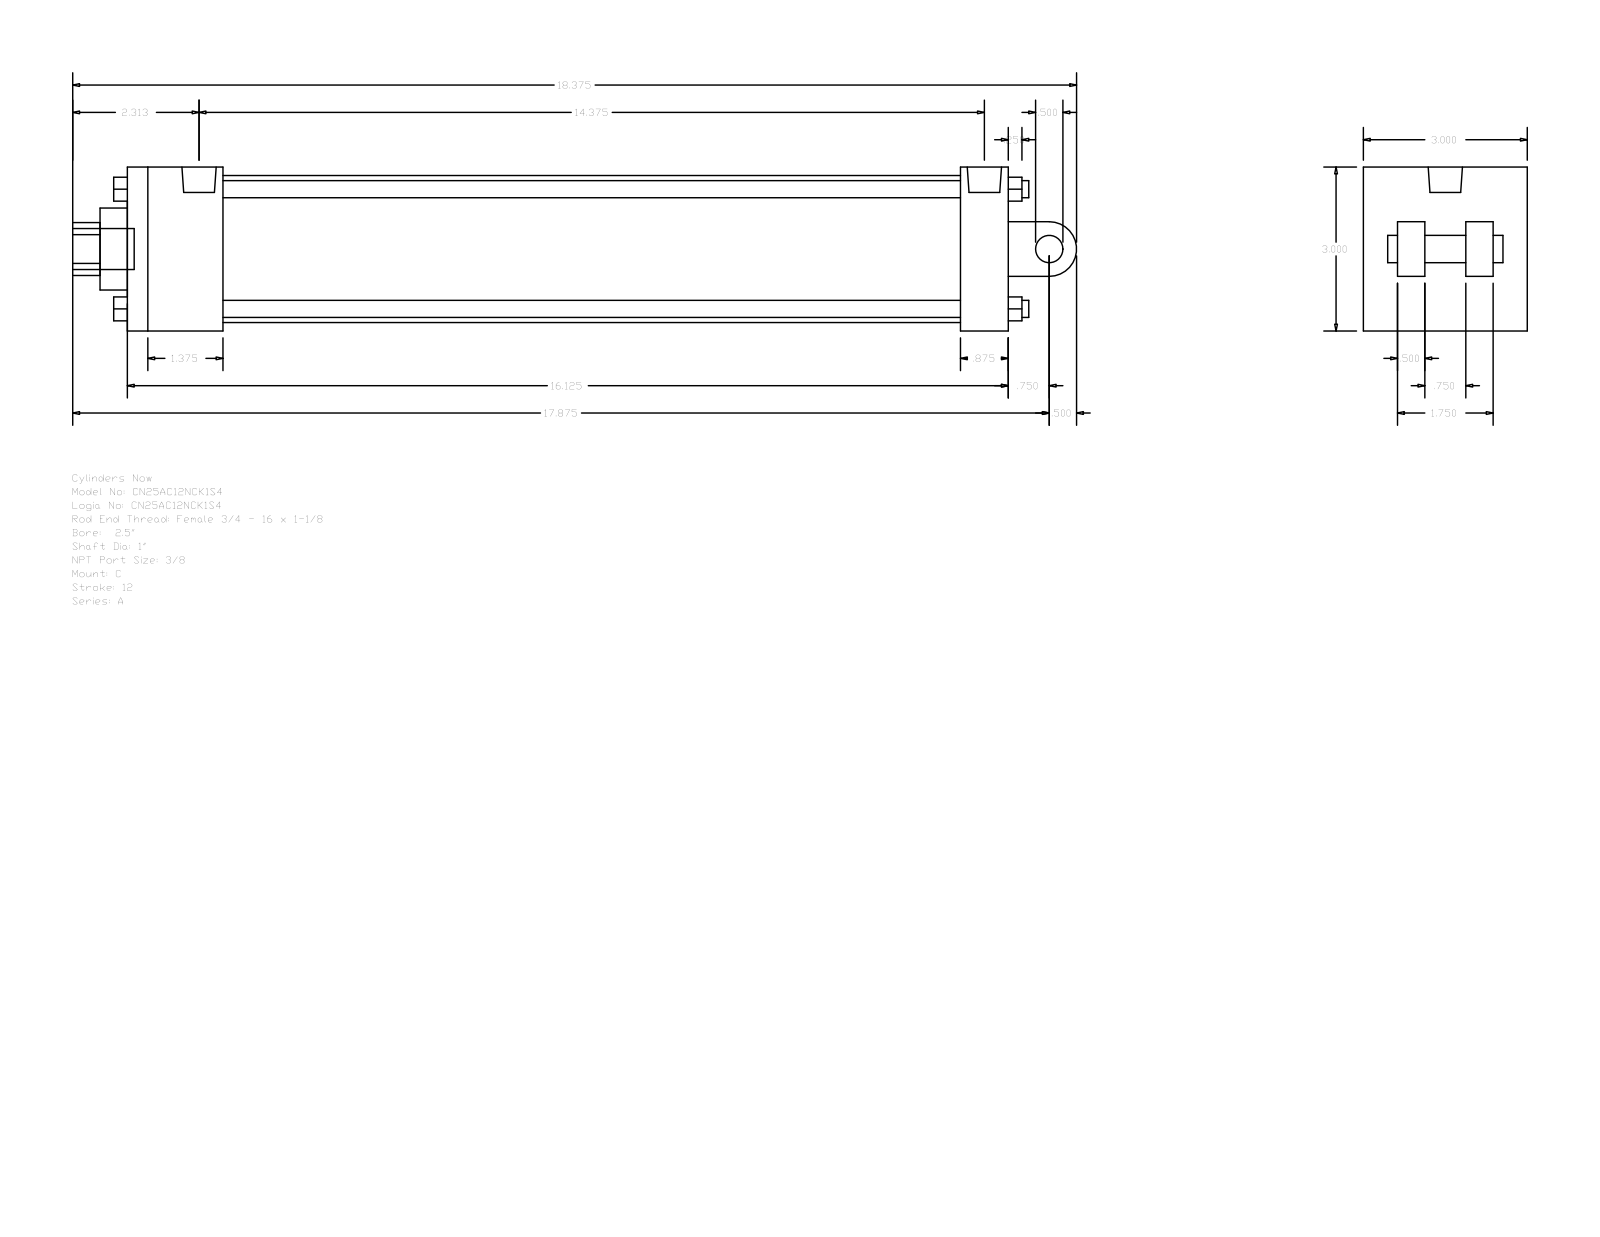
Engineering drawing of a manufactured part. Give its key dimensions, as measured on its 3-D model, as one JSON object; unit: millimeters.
{"part_name": "A_C__0250_1", "step_written_by": "GSSL Pune (CONFIG_CONTROL_DESIGN)", "units": "millimeters", "bodies": {"solids": 0, "faces": 135, "planar": 102, "cylindrical": 33, "other": 0}, "overall_size": [466.73, 76.2, 76.2], "round_holes": [[5.56, 2], [15.93, 1], [25.4, 1], [38.1, 1], [68.33, 1]], "round_bosses_or_shafts": [[7.94, 4], [5.56, 2], [19.05, 1], [15.93, 1], [12.7, 1]], "partial_cylinders_radius": [[12.29, 1], [12.7, 1]], "face_to_face_distances": [76.2, 409.58, 12.7, 44.45, 387.35, 342.9, 365.13, 22.23, 15.87, 25.4], "hole_center_spacings": [2.38]}
